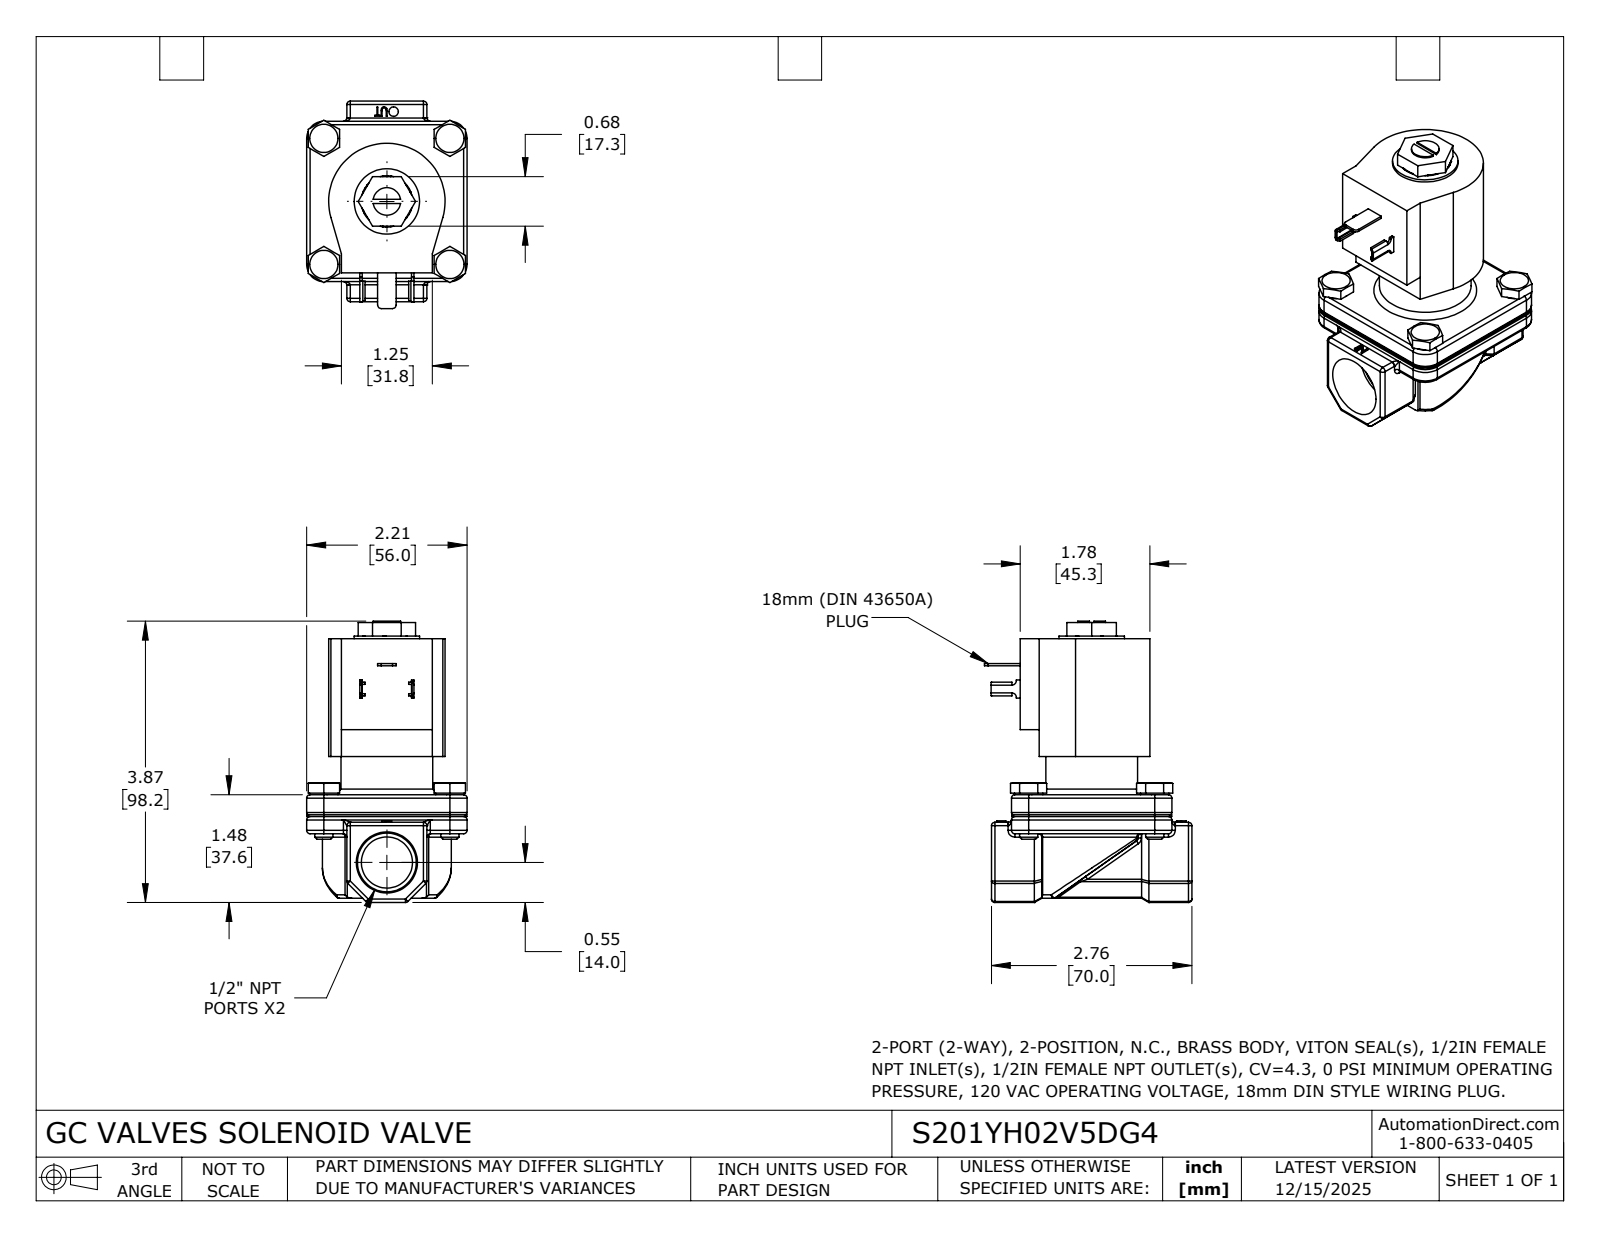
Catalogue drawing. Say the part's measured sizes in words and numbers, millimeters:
The part is named "S201YH02V5DG4". Its 3-D file was written by "SolidWorks 2024 (CONFIG_CONTROL_DESIGN)". It is 1 solid with 507 faces: 201 planar, 158 cylindrical and 148 other. Overall it measures 98.2 by 72.4 by 56 millimeters. Its volume is 154 400 cubic millimeters and its surface area 27 620 square millimeters. Round holes: 1 of diameter 17.9, 1 of diameter 17.9. Round bosses or shafts: 4 of diameter 9.9, 4 of diameter 6.4, 1 of diameter 32, 1 of diameter 22.9, 1 of diameter 11.8, 1 of diameter 9.7. Partial cylindrical surfaces (rounded edges, fillets, slot ends): 64 of radius 1.2, 4 of radius 0.2, 4 of radius 0.8, 4 of radius 1, 4 of radius 5.9, 4 of radius 6, 2 of radius 1.3, 2 of radius 1.5. The main face-to-face distances are 54.4, 1.5, 14, 42, 13.6, 68.1, 56, 26.9, 13.3, 41.1.
